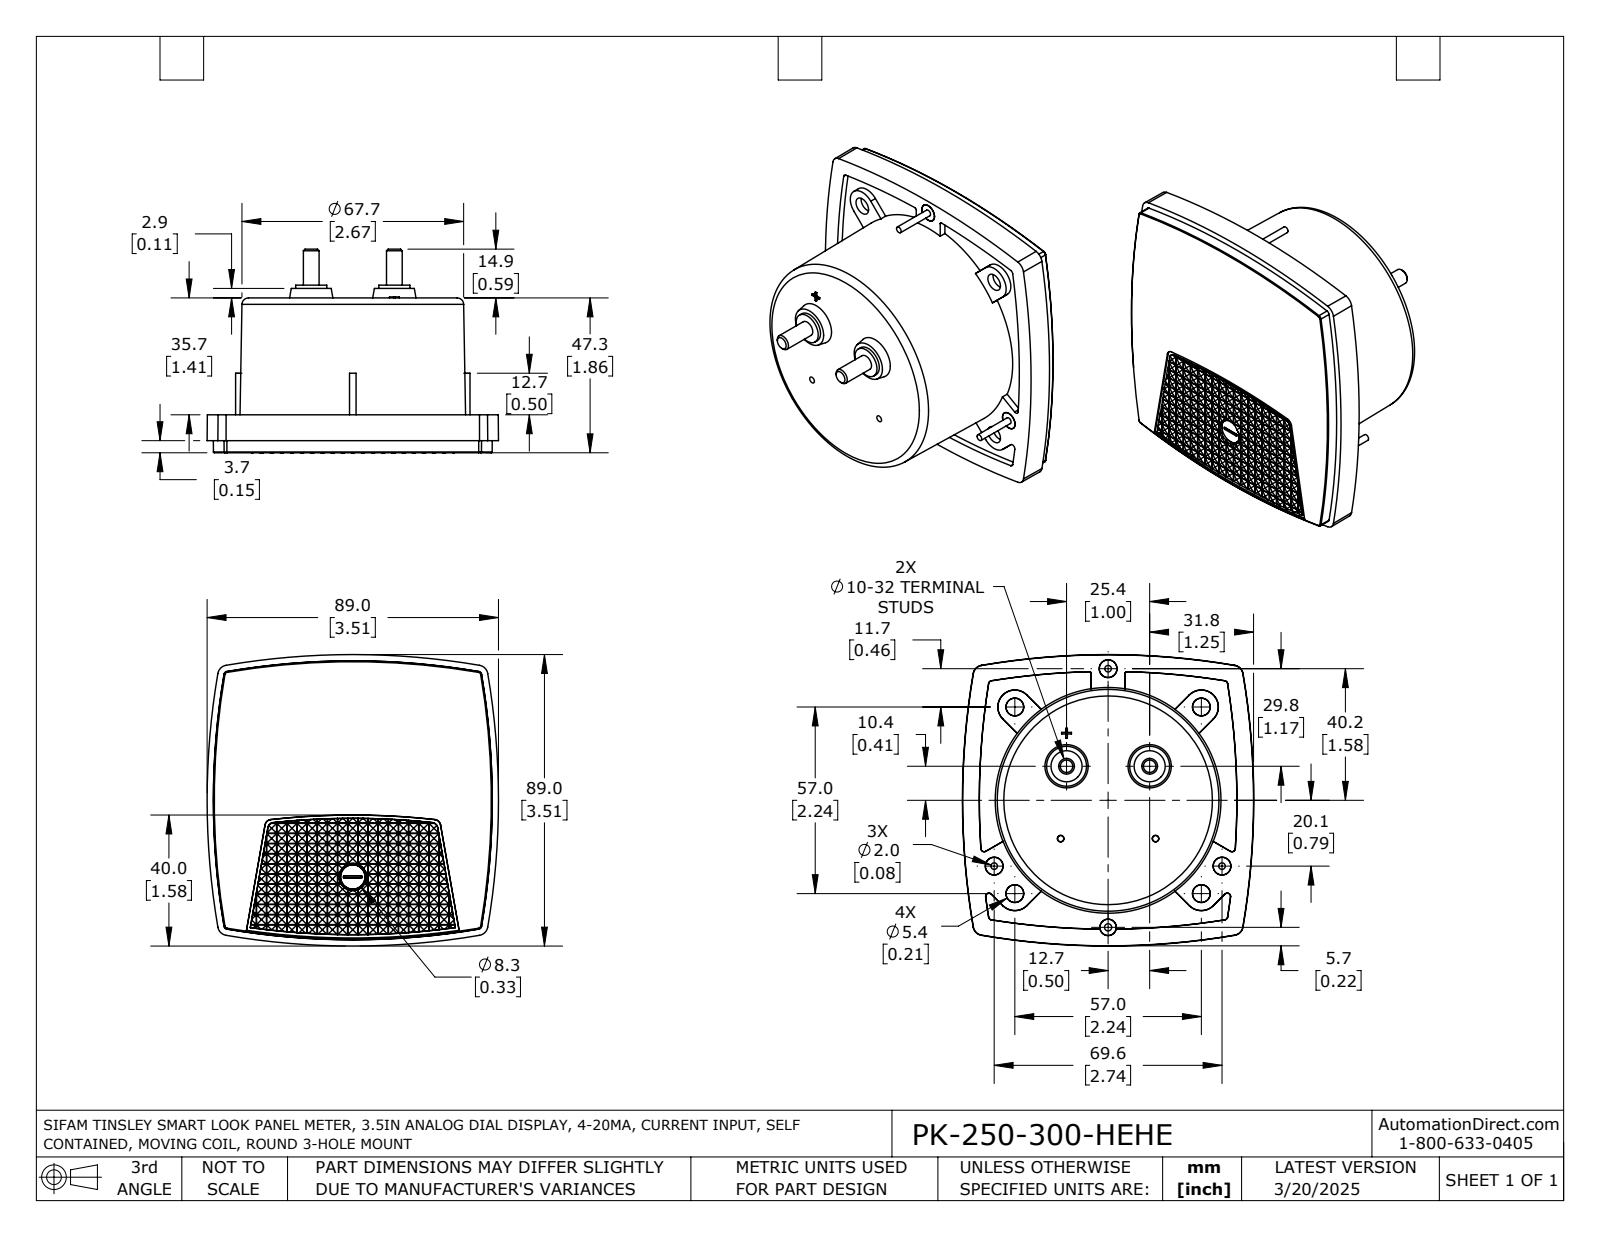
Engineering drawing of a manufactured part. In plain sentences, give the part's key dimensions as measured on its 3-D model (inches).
The part is named "PK-250-300-HEHE". Its 3-D file was written by "SolidWorks 2021 (AUTOMOTIVE_DESIGN)". It is 1 solid with 1078 faces: 950 planar, 23 cylindrical and 105 other. Overall it measures 3.505 by 3.505 by 2.453 inches. Its volume is 12.99 cubic inches and its surface area 44.29 square inches. Round holes: 1 of diameter 0.087. Round bosses or shafts: 3 of diameter 0.213, 3 of diameter 0.079, 2 of diameter 0.374, 2 of diameter 0.189. Partial cylindrical surfaces (rounded edges, fillets, slot ends): 1 of radius 8.961. The main face-to-face distances are 1.862, 1.406, 0.457, 0.079, 1.484, 0.378, 0.024, 0.096, 0.072, 0.12.
